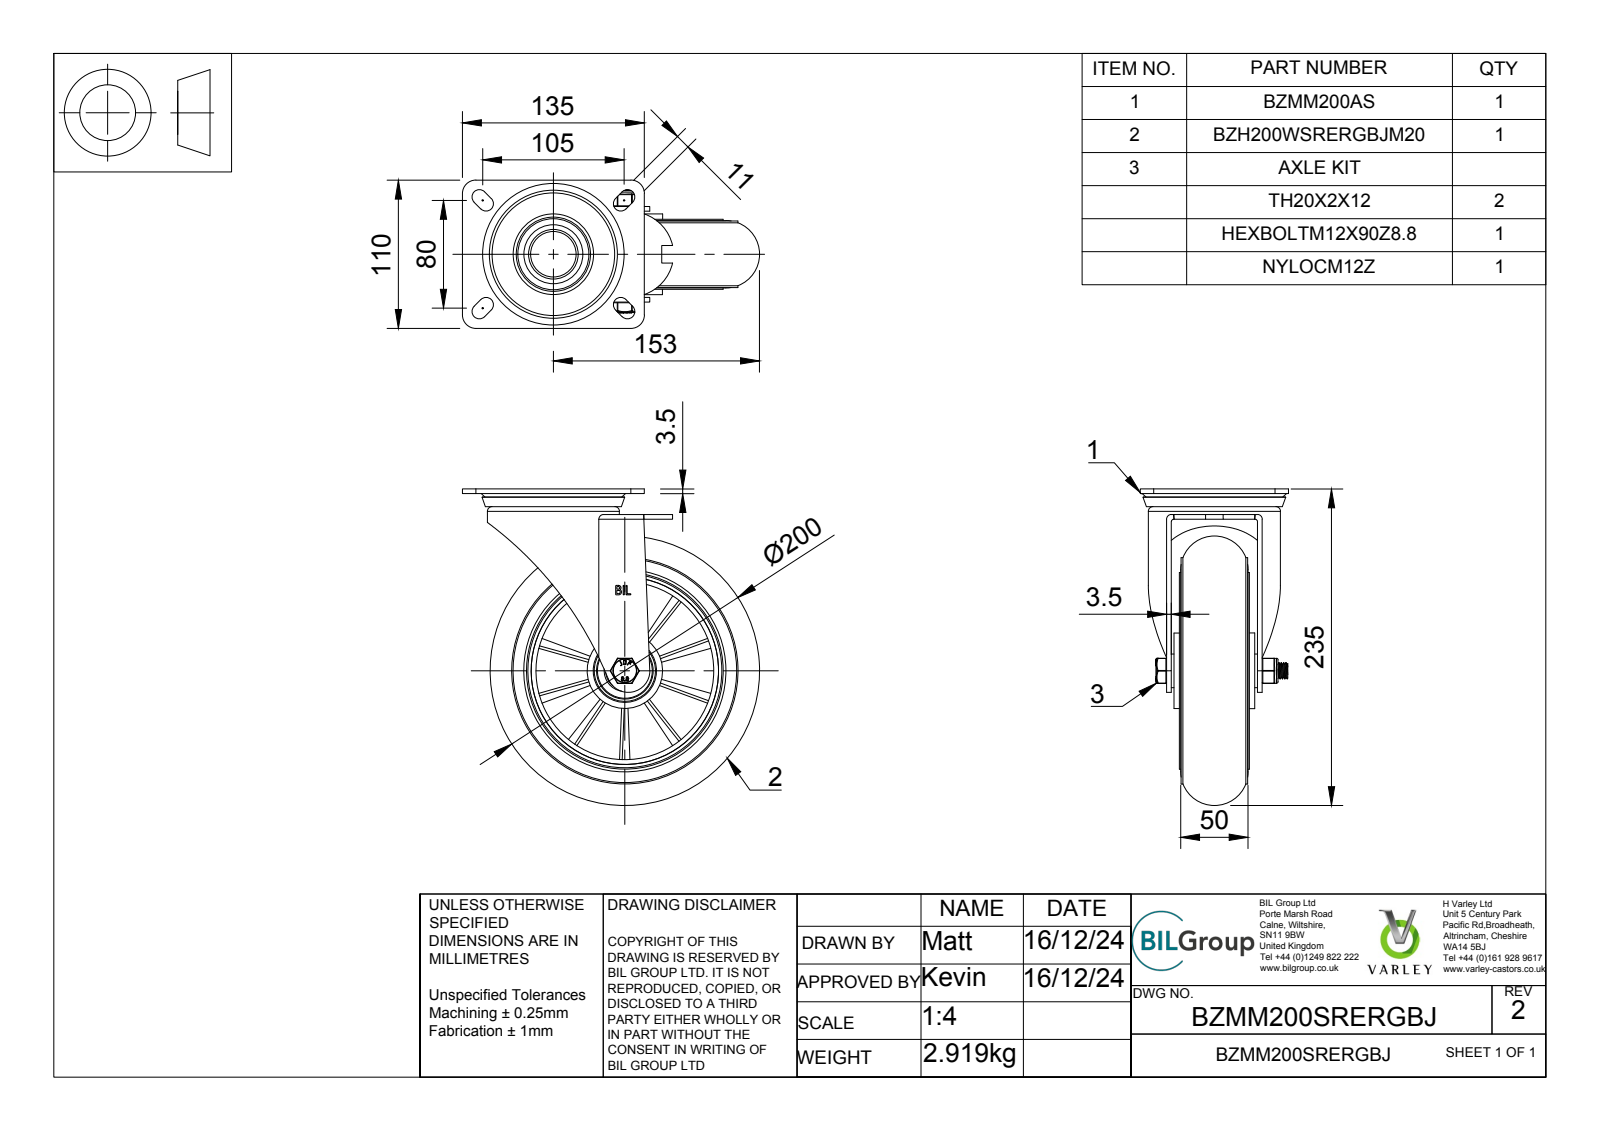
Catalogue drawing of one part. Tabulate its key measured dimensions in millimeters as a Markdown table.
| quantity | value |
| --- | --- |
| part name | BZMM200SRERGBJ - 2 v5; BZMM200AS - 2 - 64 v1; ZINC PLATED, PRESSED STEEL TOP PLATE; ZINC PLATED, PRESSED STEEL TOP PLATE Geometry (+7 more) |
| STEP written by | Autodesk Translation Framework v13.20.0.188 (AP242_MANAGED_MODEL_BASED_3D_ENGINEERING_MIM_LF) |
| units | millimeters |
| bodies | 77 solids, 1217 faces (488 planar, 218 cylindrical, 511 other) |
| overall size | 235 × 220.5 × 110 |
| volume | 1 057 000 mm³ |
| surface area | 340 885 mm² |
| round holes (diameter × count) | 12 × 1, 12.2 × 1, 14 × 1, 20 × 1, 28.5 × 1, 30.8 × 1, 33.75 × 1, 40.3 × 1, 40.5 × 1, 42 × 1, 47 × 1, 55 × 1 |
| round bosses / shafts (diameter × count) | 168 × 1, 146 × 1, 98 × 1, 78 × 1, 56.2 × 1, 56 × 1, 50 × 1, 40.8 × 1 |
| partial cylindrical surfaces (radius × count) | 0.5 × 19, 5.5 × 8, 0.47 × 4, 0.9 × 4, 1.75 × 4, 10 × 4, 0.89 × 2, 0.89 × 2 |
| main face-to-face distances | 3.5, 2, 14.25, 47.75, 16.25, 17.75, 9, 49.75, 33.5, 19.75 |
